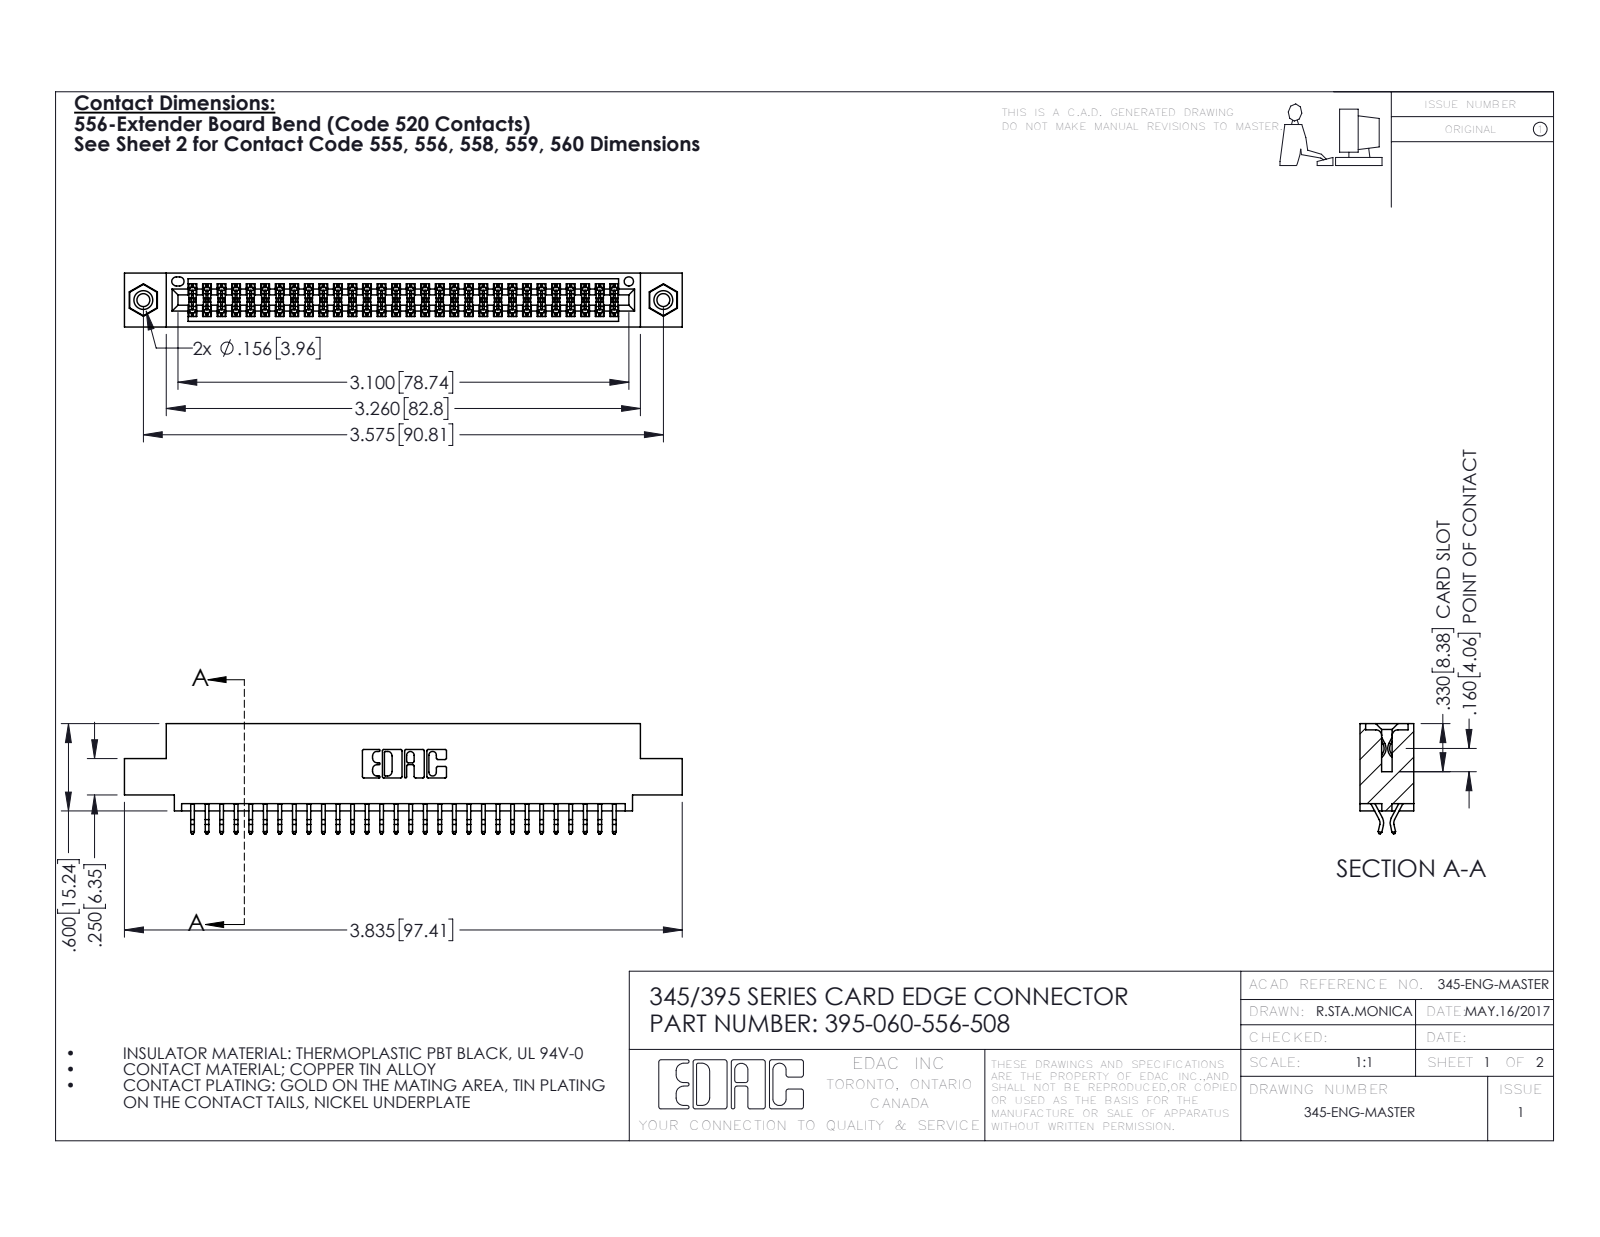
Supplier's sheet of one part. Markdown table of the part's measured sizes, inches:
| quantity | value |
| --- | --- |
| part name | 395-060-556-508; 345-250-001_345-250-003-102; 345 Part_0.110 Offset - 0.156 Dia-TI; 345-292-001_556 Tail |
| STEP written by | SolidWorks 2016 (CONFIG_CONTROL_DESIGN) |
| units | inches |
| bodies | 63 solids, 3550 faces (2336 planar, 1198 cylindrical, 16 other) |
| overall size | 3.835 × 0.757 × 0.37 |
| volume | 0.566 in³ |
| surface area | 20.96 in² |
| round holes (diameter × count) | 0.089 × 2, 0.125 × 2, 0.156 × 2, 0.064 × 1 |
| round bosses / shafts (diameter × count) | 0.155 × 2 |
| partial cylindrical surfaces (radius × count) | 0.006 × 90, 0.01 × 22, 0.007 × 6, 0.031 × 6, 0.026 × 3, 0.01 × 2, 0.014 × 2, 0.019 × 2 |
| main face-to-face distances | 0.072, 0.298, 0.37, 0.2, 0.025, 0.098, 0.272, 0.225, 0.175, 0.149 |
| hole center spacings | 0.27, 3.34, 3.575 |
